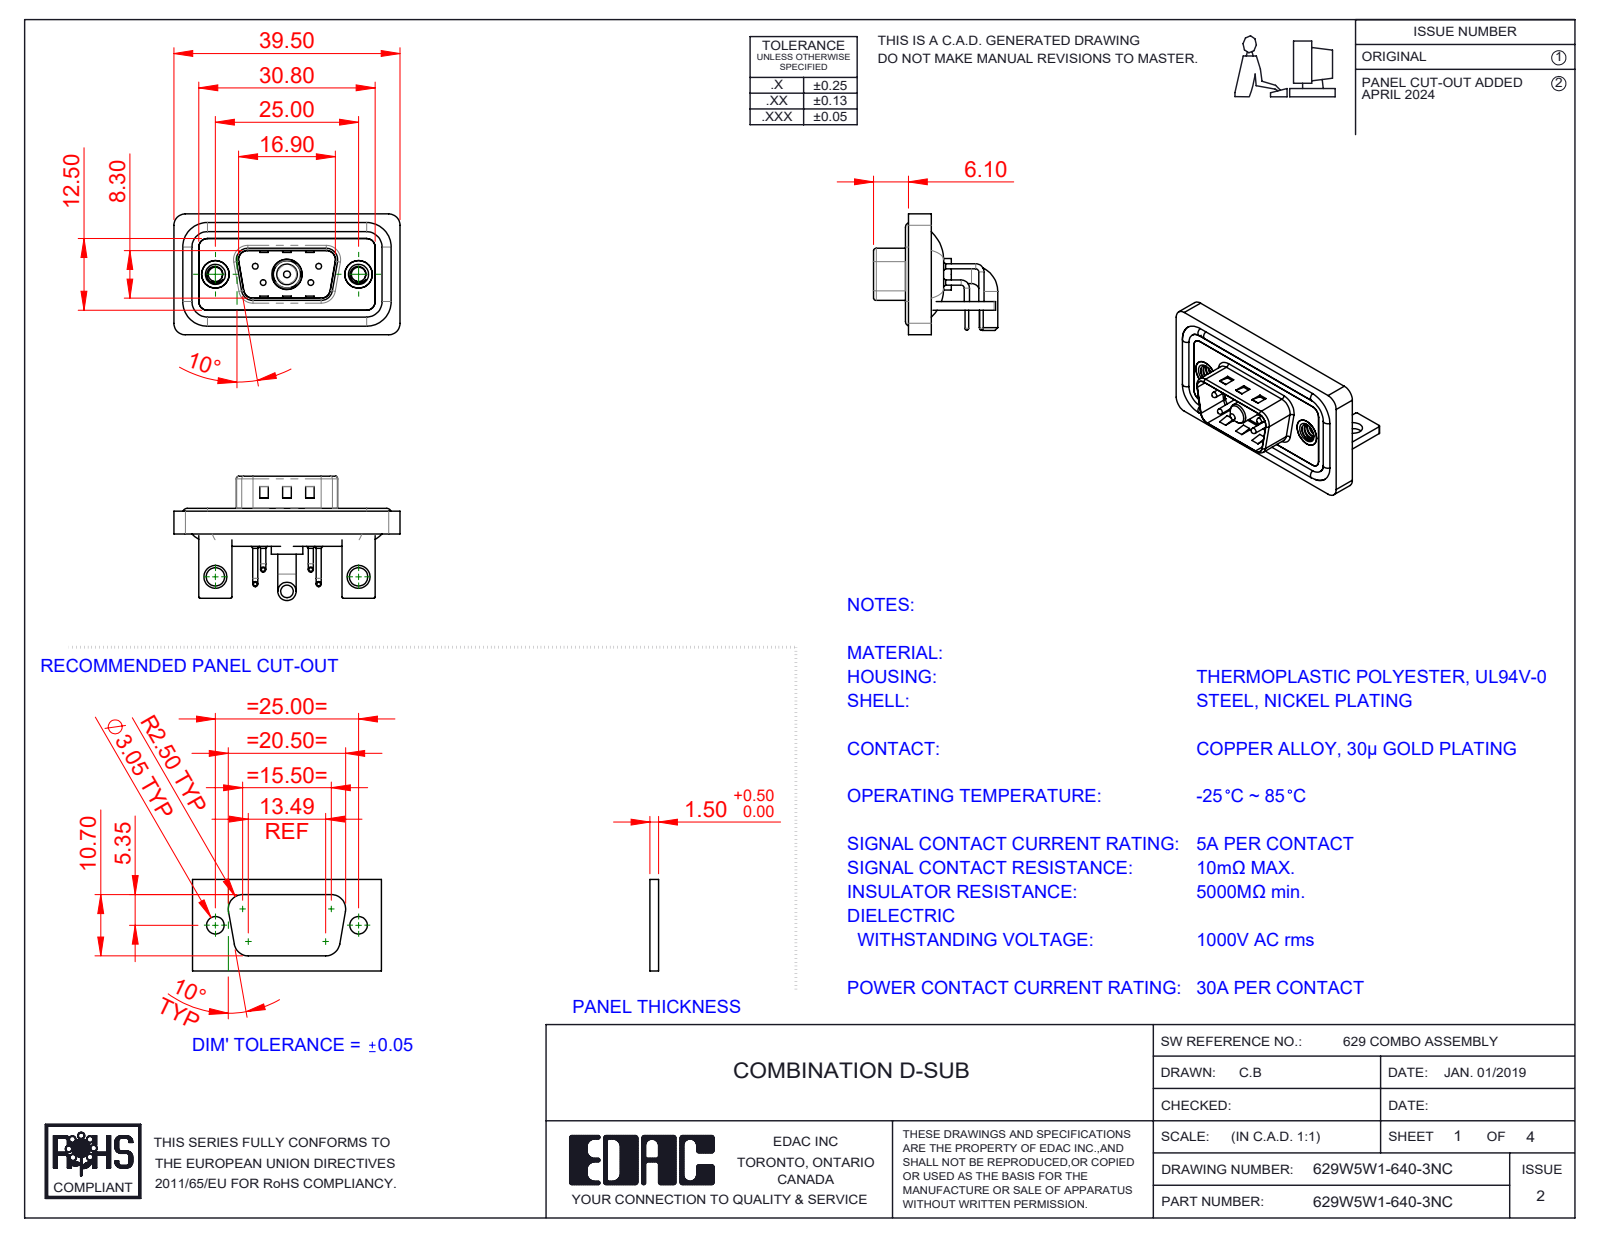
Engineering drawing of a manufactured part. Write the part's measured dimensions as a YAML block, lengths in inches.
part_name: "629Combo Contact Row 2; 629Combo Contact Row 1; Power Pin_30A RA; 629Combo Shell Front_09 Contacts (+6 more)"
step_written_by: "SolidWorks 2023 (CONFIG_CONTROL_DESIGN)"
units: inches
bodies: {solids: 15, faces: 932, planar: 431, cylindrical: 363, other: 138}
overall_size: [1.555, 0.854, 0.831]
volume: 0.291
surface_area: 12.04
round_holes:
  - {diameter: 0.03, count: 4}
  - {diameter: 0.063, count: 4}
  - {diameter: 0.079, count: 4}
  - {diameter: 0.098, count: 2}
  - {diameter: 0.126, count: 2}
  - {diameter: 0.157, count: 2}
  - {diameter: 0.189, count: 2}
  - {diameter: 0.197, count: 2}
  - {diameter: 0.191, count: 1}
  - {diameter: 0.209, count: 1}
round_bosses_or_shafts:
  - {diameter: 0.035, count: 8}
  - {diameter: 0.063, count: 4}
  - {diameter: 0.059, count: 4}
  - {diameter: 0.039, count: 4}
  - {diameter: 0.026, count: 4}
  - {diameter: 0.193, count: 2}
  - {diameter: 0.126, count: 2}
  - {diameter: 0.217, count: 1}
partial_cylinders:
  - {radius: 0.079, count: 19}
  - {radius: 0.059, count: 18}
  - {radius: 0.01, count: 16}
  - {radius: 0.02, count: 9}
  - {radius: 0.063, count: 8}
  - {radius: 0.024, count: 4}
  - {radius: 0.026, count: 4}
  - {radius: 0.035, count: 4}
face_to_face_distances: [0.016, 0.059, 0.031, 0.114, 0.043, 0.083, 0.047, 0.063, 0.098, 0.146]
hole_center_spacings: [0.124, 0.225, 0.28, 0.492, 0.713, 0.984, 0.173, 0.173]
